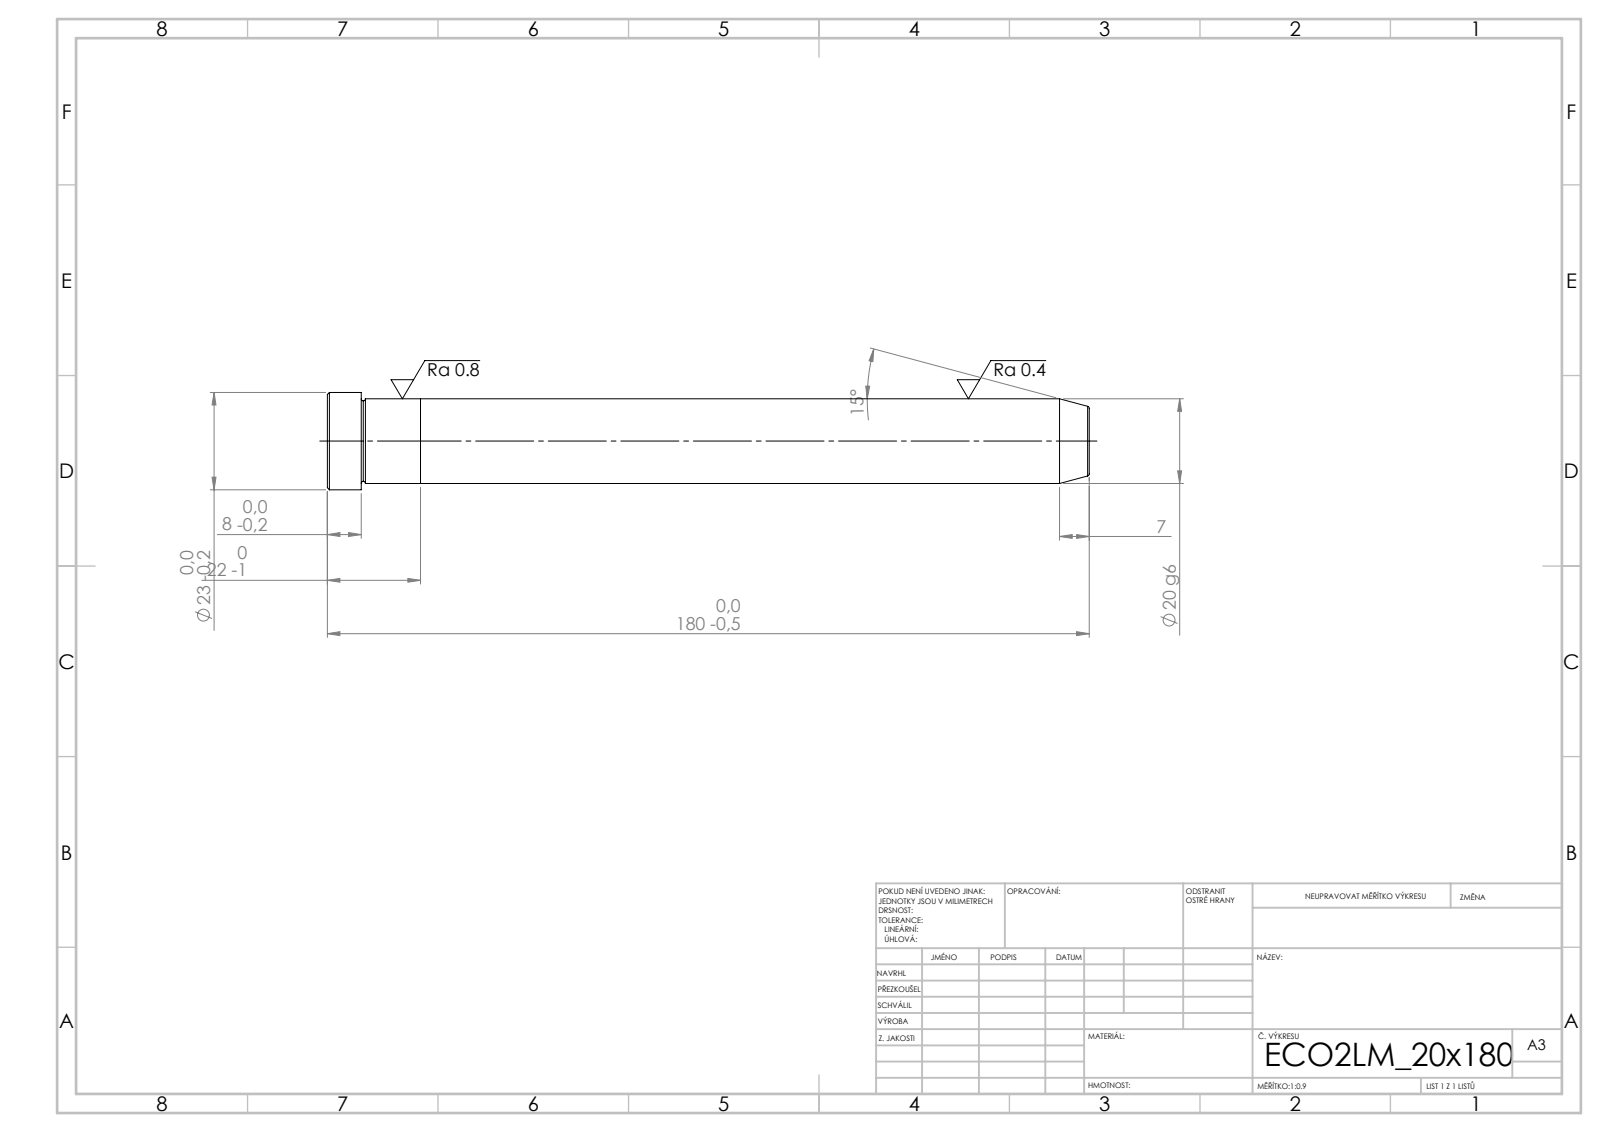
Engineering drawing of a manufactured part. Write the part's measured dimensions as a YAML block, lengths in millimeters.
step_written_by: "SolidWorks 2019 (CONFIG_CONTROL_DESIGN)"
units: millimeters
bodies: {solids: 2, faces: 21, planar: 5, cylindrical: 6, other: 10}
overall_size: [180, 23, 23]
volume: 56938
surface_area: 12716
round_bosses_or_shafts:
  - {diameter: 23, count: 1}
  - {diameter: 20, count: 1}
face_to_face_distances: [22, 158, 180, 172, 14, 8]
